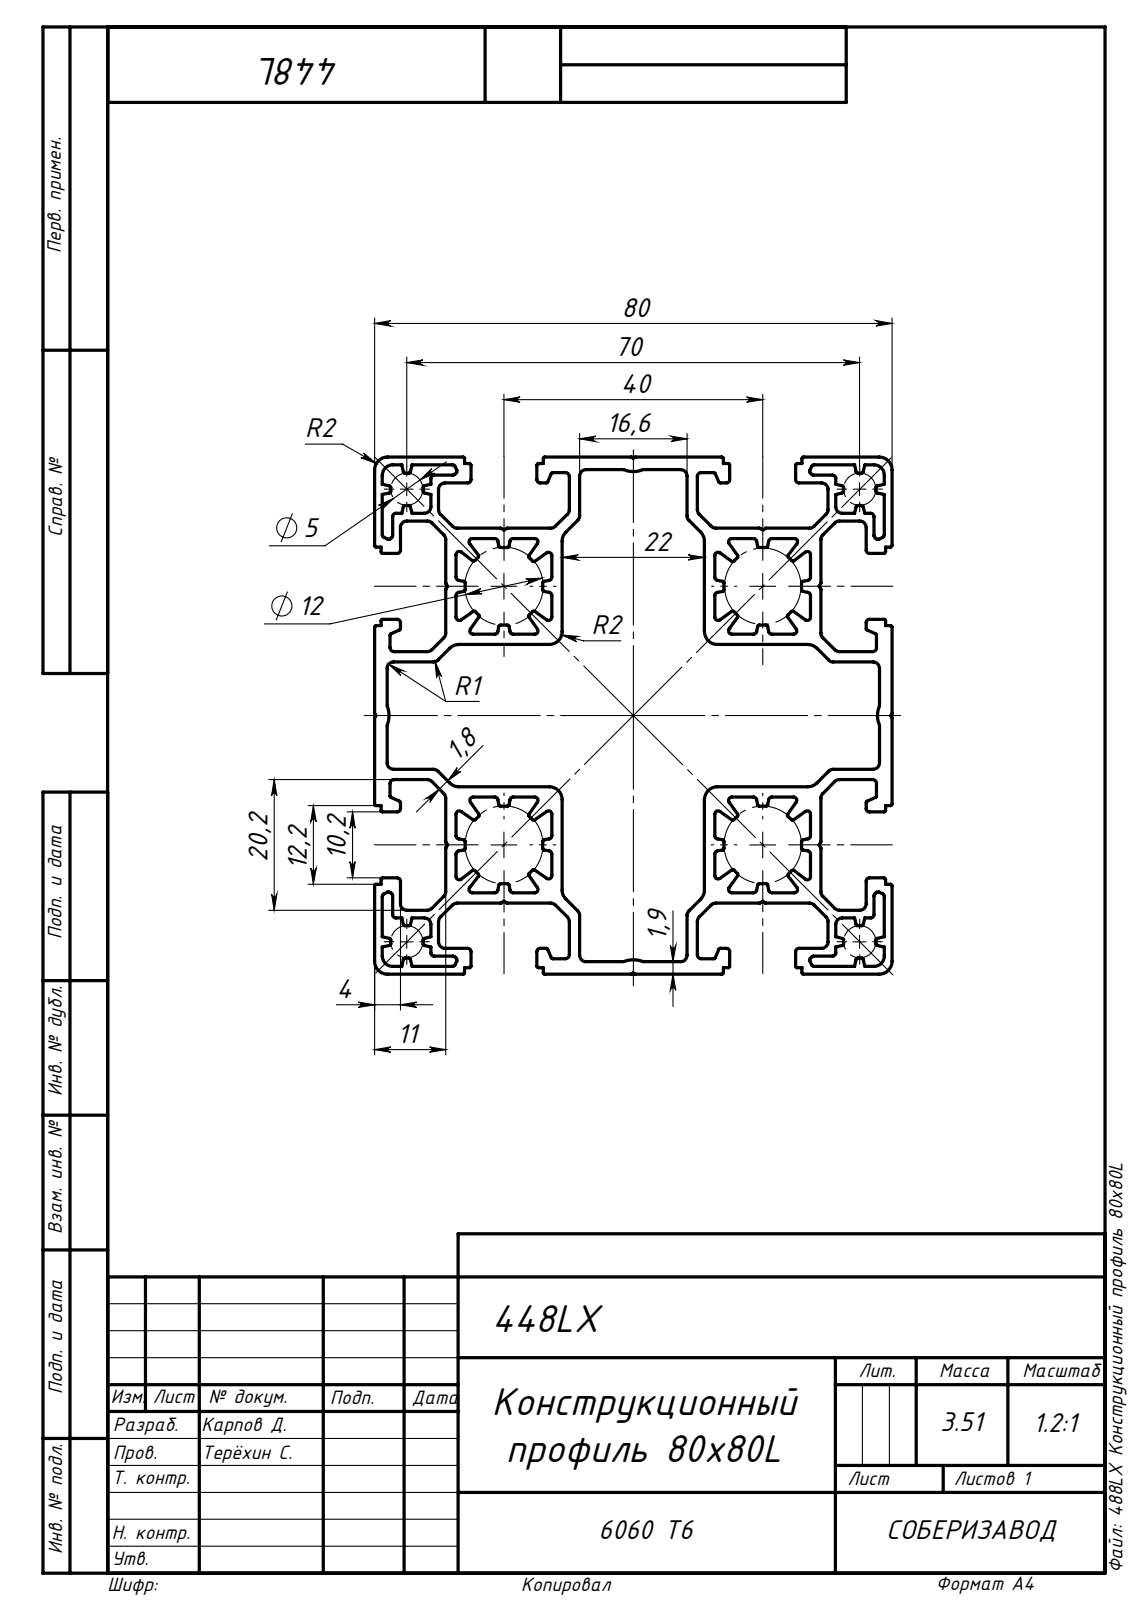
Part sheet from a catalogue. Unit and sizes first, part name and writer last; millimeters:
Units: millimetres
Overall size (bounding box): 1000 × 80 × 80
Partial cylindrical surfaces — rounded edges, fillets, slot ends (radius × count): R0.25 ×168, R0.5 ×88, R1 ×60, R0.4 ×24, R2 ×16, R0.6 ×8, R1.6 ×4, R4 ×4
Main face-to-face distances: 40, 1.6, 51, 29, 16.4, 11, 69, 18, 80, 19.1
Volume: 1 301 000 mm³ · Surface area: 1 443 000 mm²
Bodies: 1 solid, 830 faces (434 planar, 396 cylindrical, 0 other)
STEP written by: SolidWorks 2019 (AUTOMOTIVE_DESIGN)
